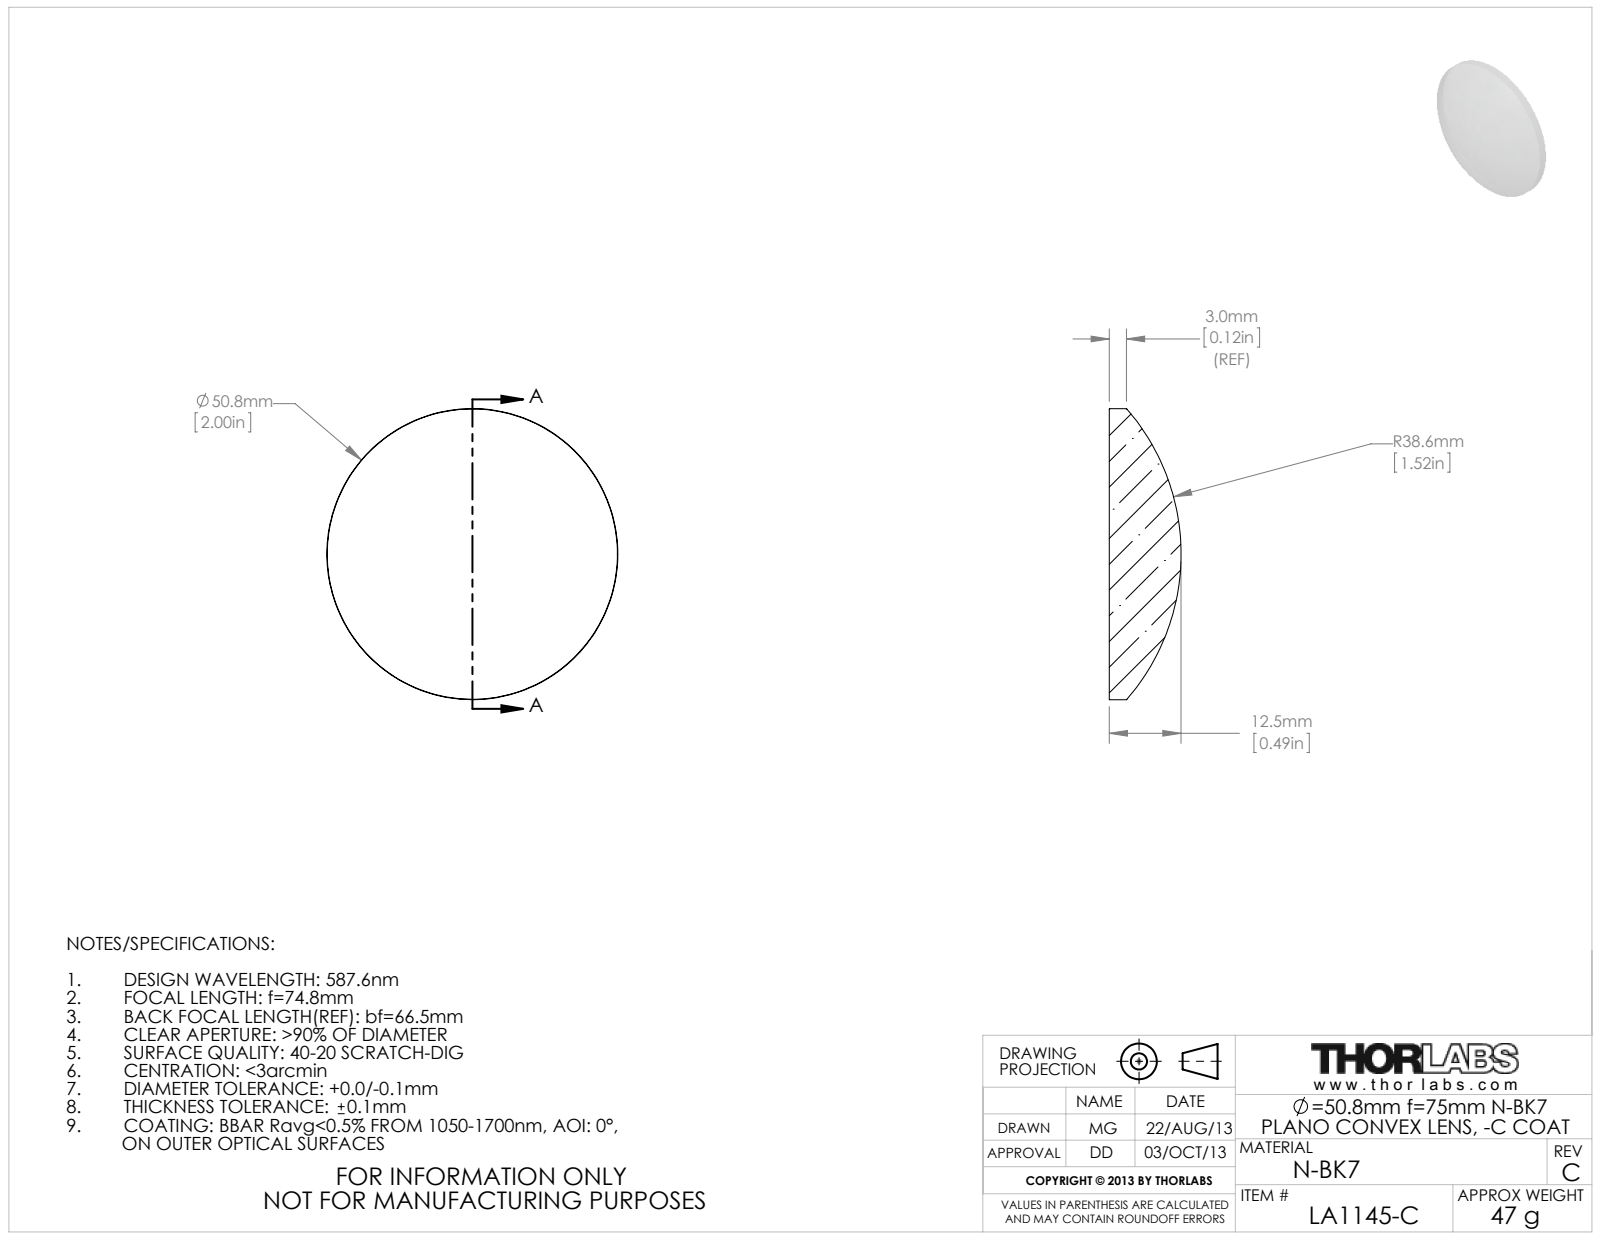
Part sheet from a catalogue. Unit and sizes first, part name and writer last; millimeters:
Units: millimetres
Overall size (bounding box): 50.8 × 50.8 × 12.52
Round bosses / shafts (diameter × count): ⌀50.8 ×1
Bodies: 0 solids, 5 faces (1 planar, 2 cylindrical, 2 other)
Part name (STEP PRODUCT): 4601-E0W
STEP written by: SolidWorks 2009 (AUTOMOTIVE_DESIGN)
